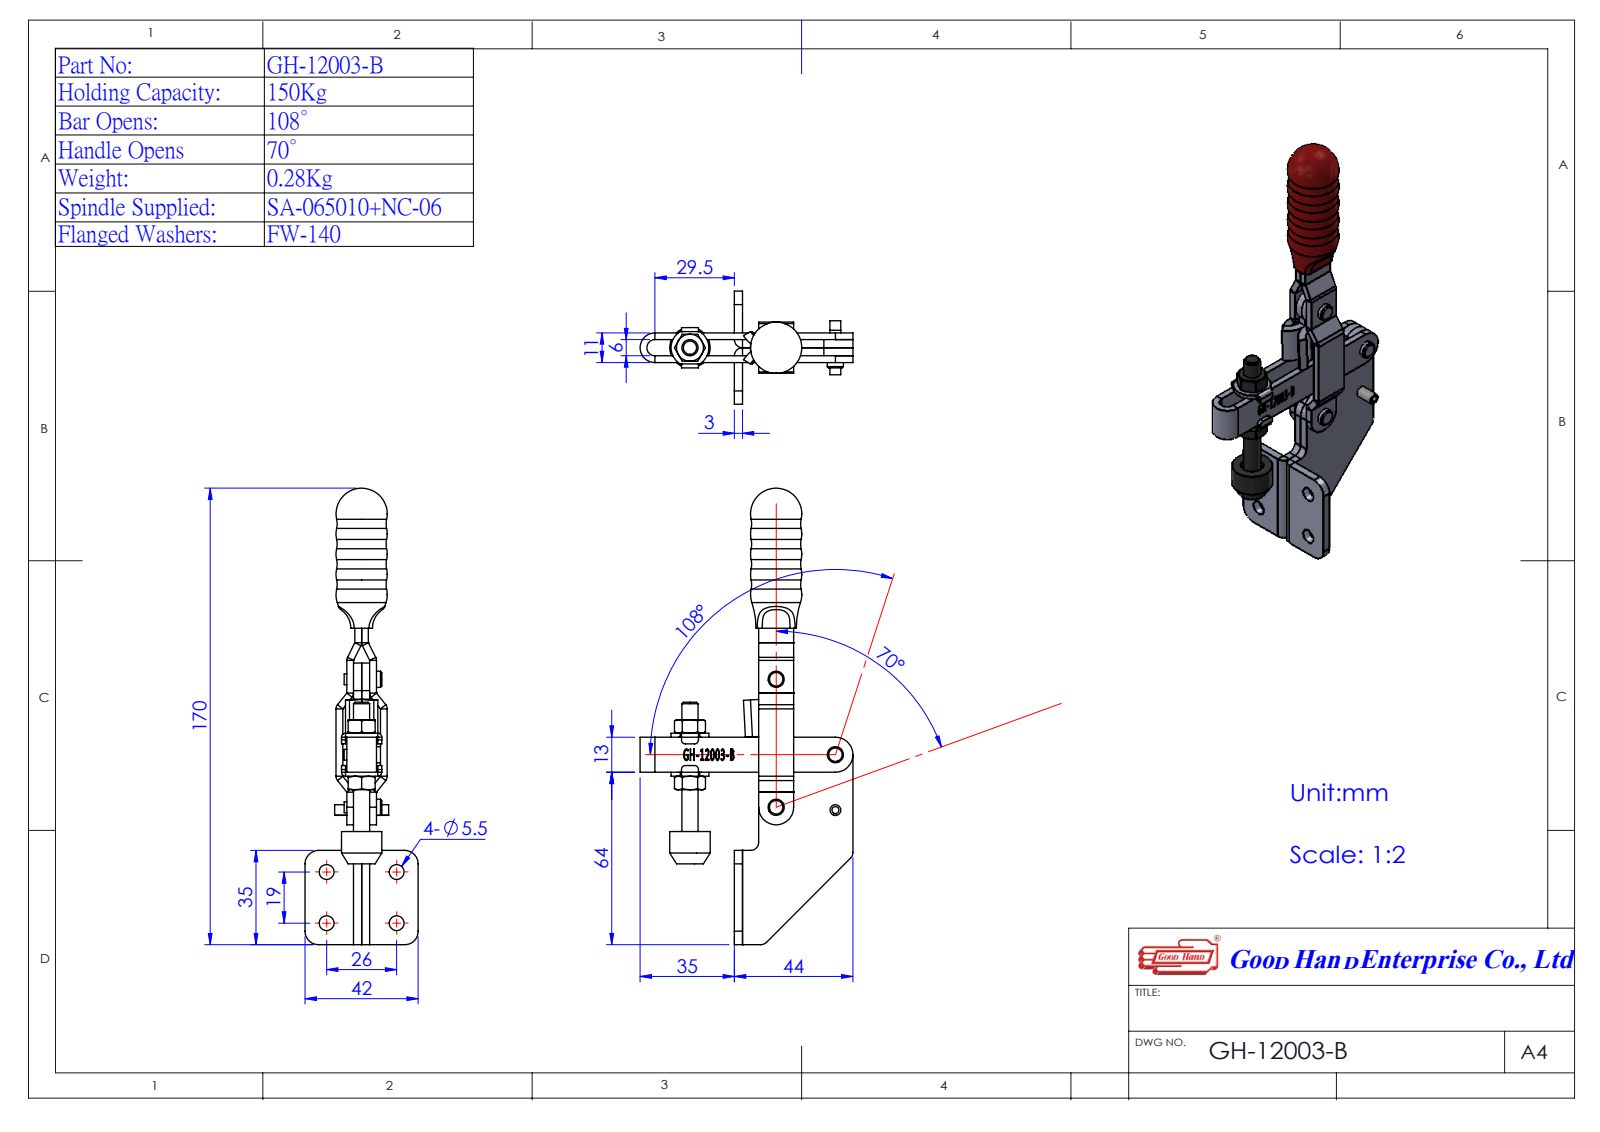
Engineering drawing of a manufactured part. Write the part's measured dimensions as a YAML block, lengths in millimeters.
part_name: "GH-12003-B(簡化)-1; Group2^GH-12003-B(簡化)-1; Group4^GH-12003-B(簡化)-1; Group5^GH-12003-B(簡化)-1 (+3 more)"
step_written_by: "SolidWorks 2016 (AUTOMOTIVE_DESIGN)"
units: millimeters
bodies: {solids: 7, faces: 332, planar: 130, cylindrical: 116, other: 86}
overall_size: [170, 79, 42]
volume: 49693
surface_area: 27592
round_holes:
  - {diameter: 3, count: 4}
  - {diameter: 5.5, count: 4}
  - {diameter: 5, count: 1}
  - {diameter: 6, count: 1}
  - {diameter: 6.3, count: 1}
  - {diameter: 11.5, count: 1}
round_bosses_or_shafts:
  - {diameter: 15, count: 1}
  - {diameter: 4.1, count: 1}
partial_cylinders:
  - {radius: 1, count: 4}
  - {radius: 2, count: 4}
  - {radius: 2.6, count: 4}
  - {radius: 5, count: 4}
  - {radius: 6, count: 4}
  - {radius: 0.5, count: 2}
  - {radius: 6.5, count: 2}
  - {radius: 9, count: 2}
face_to_face_distances: [6, 2.5, 8.5, 4, 12.5, 3, 11, 13, 10, 6.5]
hole_center_spacings: [19, 26, 32.2, 19.56, 20.53, 28.04, 29.4, 35.63]
